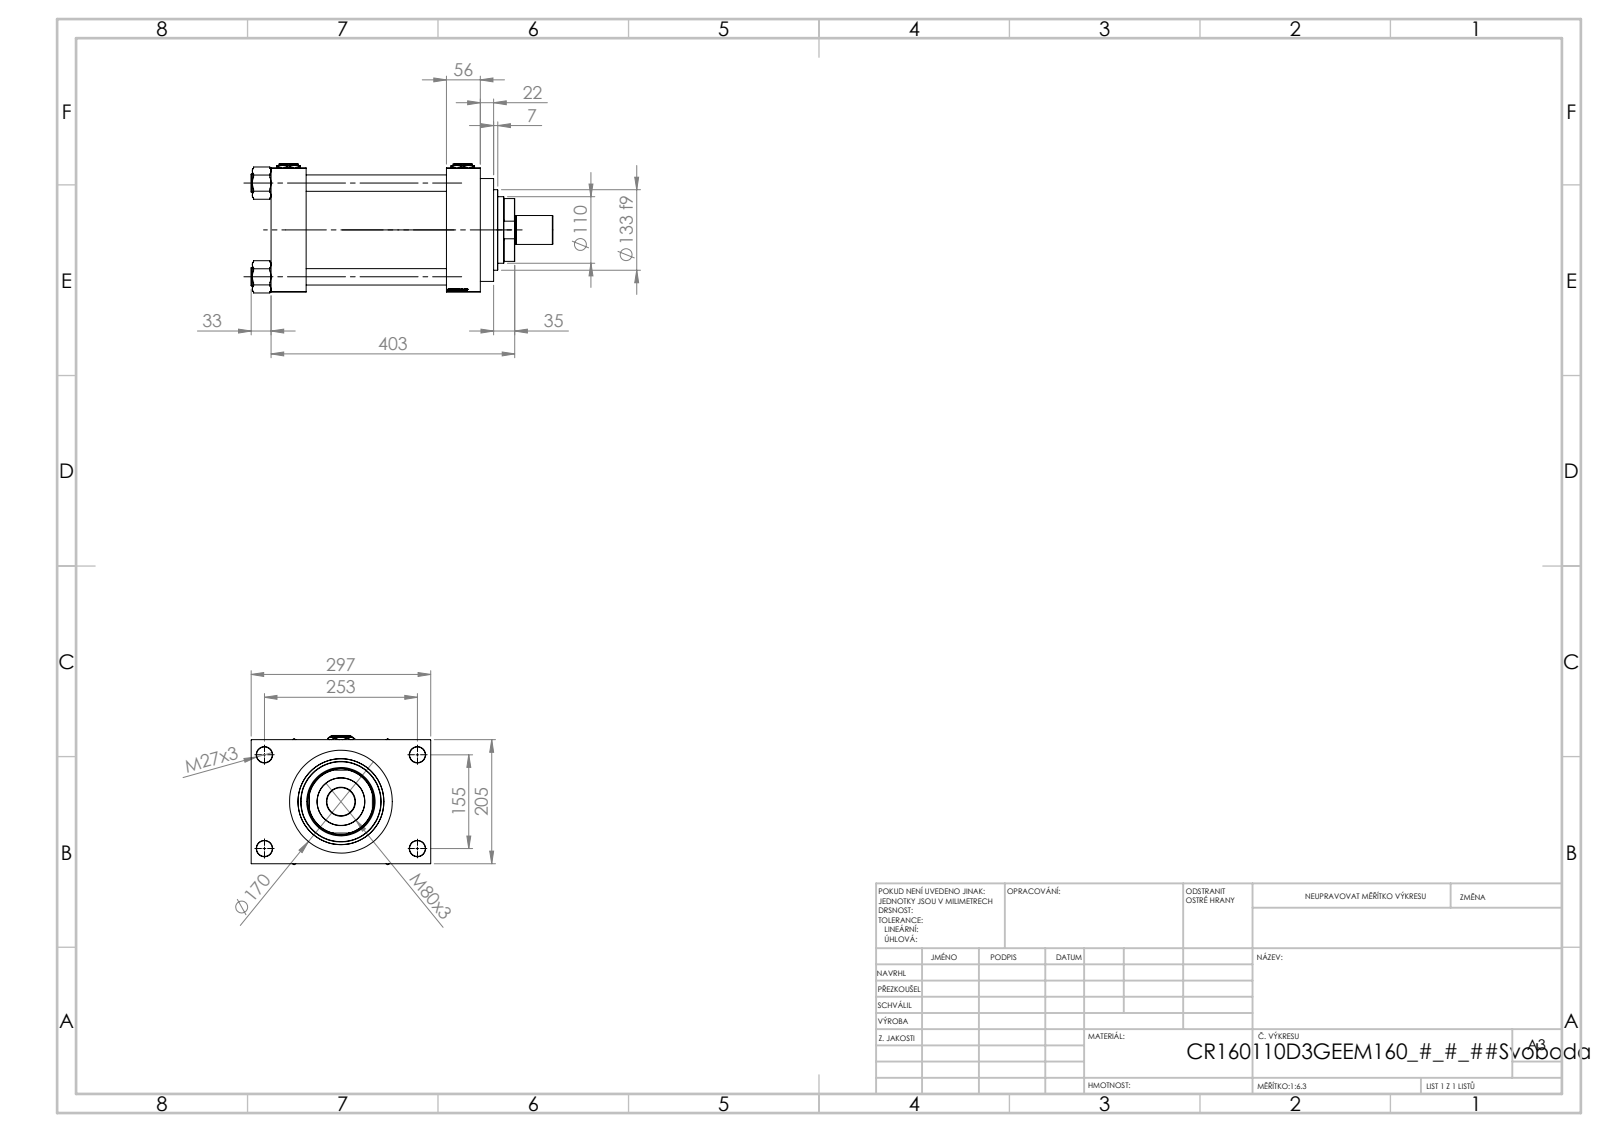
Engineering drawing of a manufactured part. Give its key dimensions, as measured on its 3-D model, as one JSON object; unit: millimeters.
{"part_name": "V215CR_VCP_D; ROD_END_E; V215_VC_A; V215CR_D_Body (+3 more)", "step_written_by": "SolidWorks 2019 (CONFIG_CONTROL_DESIGN)", "units": "millimeters", "bodies": {"solids": 14, "faces": 1267, "planar": 597, "cylindrical": 104, "other": 566}, "overall_size": [499, 297, 213.57], "volume_mm3": 10110000, "surface_area_mm2": 1039000, "round_holes": [[26, 4], [27, 4], [7, 2], [33.24, 2], [45, 2], [78.5, 1], [110, 1], [113, 1], [120, 1], [142, 1], [160, 1]], "round_bosses_or_shafts": [[30, 4], [170, 1], [166, 1], [133, 1], [48, 1], [46, 1]], "partial_cylinders_radius": [[54, 1]], "face_to_face_distances": [58, 290, 232, 205, 56, 346, 288, 46, 251, 72], "hole_center_spacings": [49.05, 109.53, 148.35, 154.9, 162.53, 203.95, 256.13, 155]}
